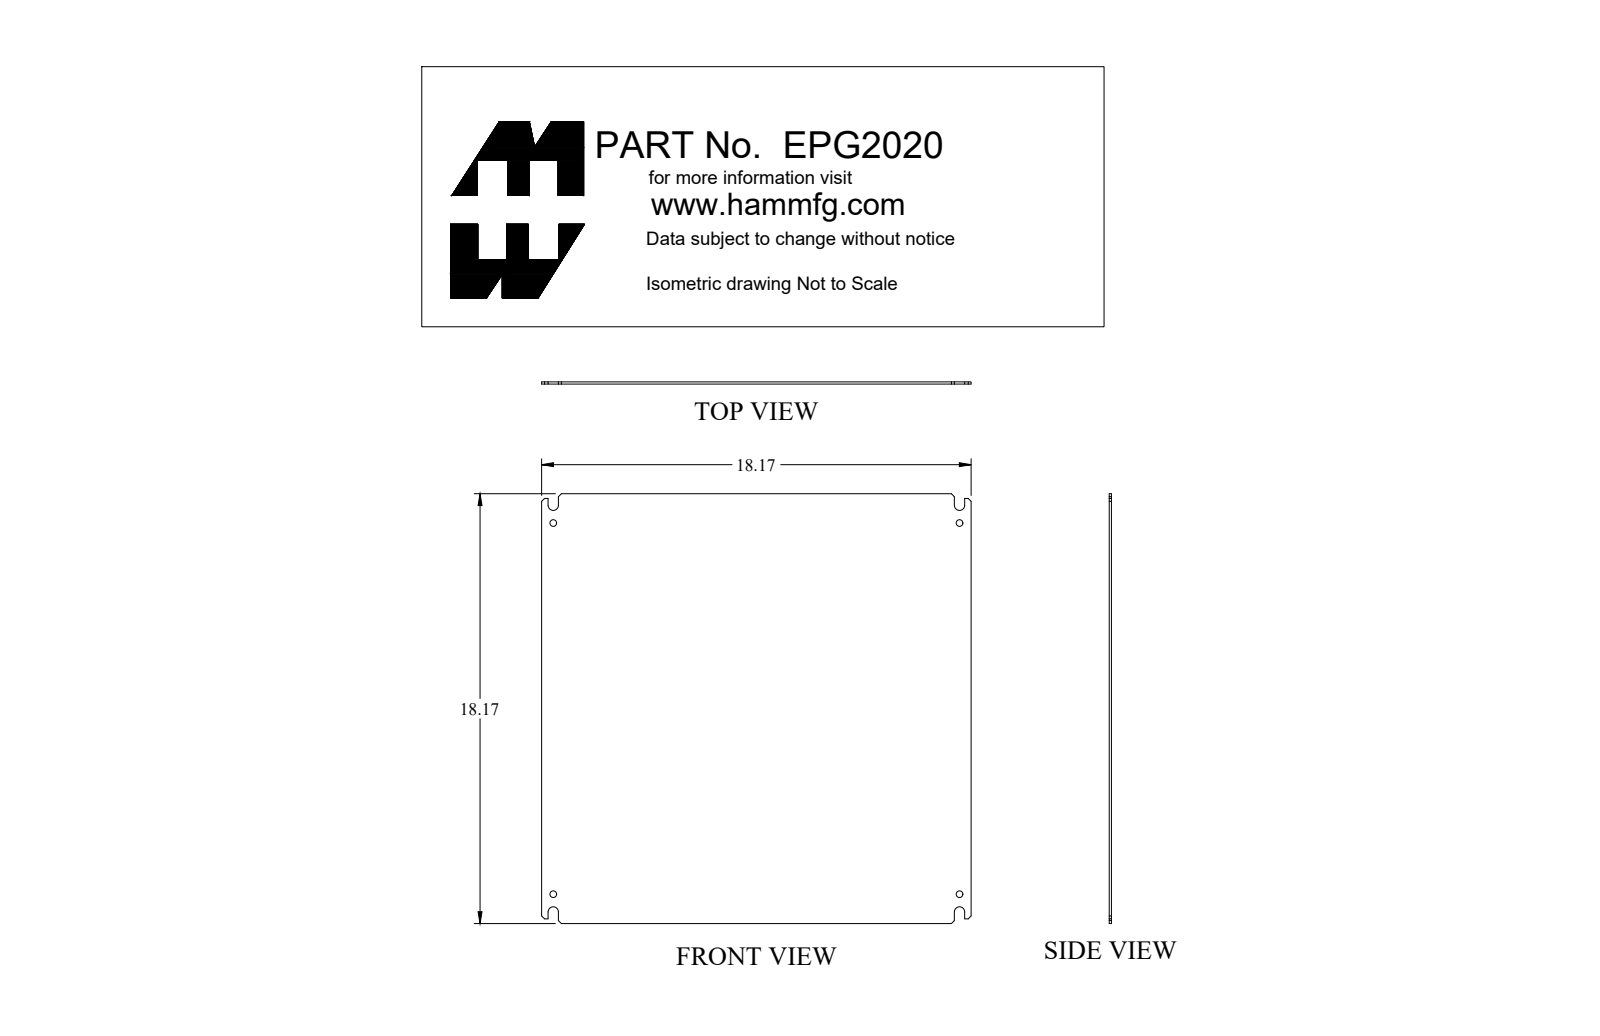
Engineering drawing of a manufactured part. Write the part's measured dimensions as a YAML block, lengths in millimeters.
part_name: "EPG2020"
step_written_by: "SolidWorks 2018 (AUTOMOTIVE_DESIGN)"
units: millimeters
bodies: {solids: 1, faces: 40, planar: 26, cylindrical: 14, other: 0}
overall_size: [461.5, 461.5, 2.4]
volume: 511300
surface_area: 428600
round_holes:
  - {diameter: 7.1, count: 4}
partial_cylinders:
  - {radius: 5.6, count: 4}
face_to_face_distances: [2.4, 461.5, 18, 443.5, 6.9, 454.6, 11.1, 436.6, 425.5, 9.2]
hole_center_spacings: [398.5, 436.6, 591.1]
